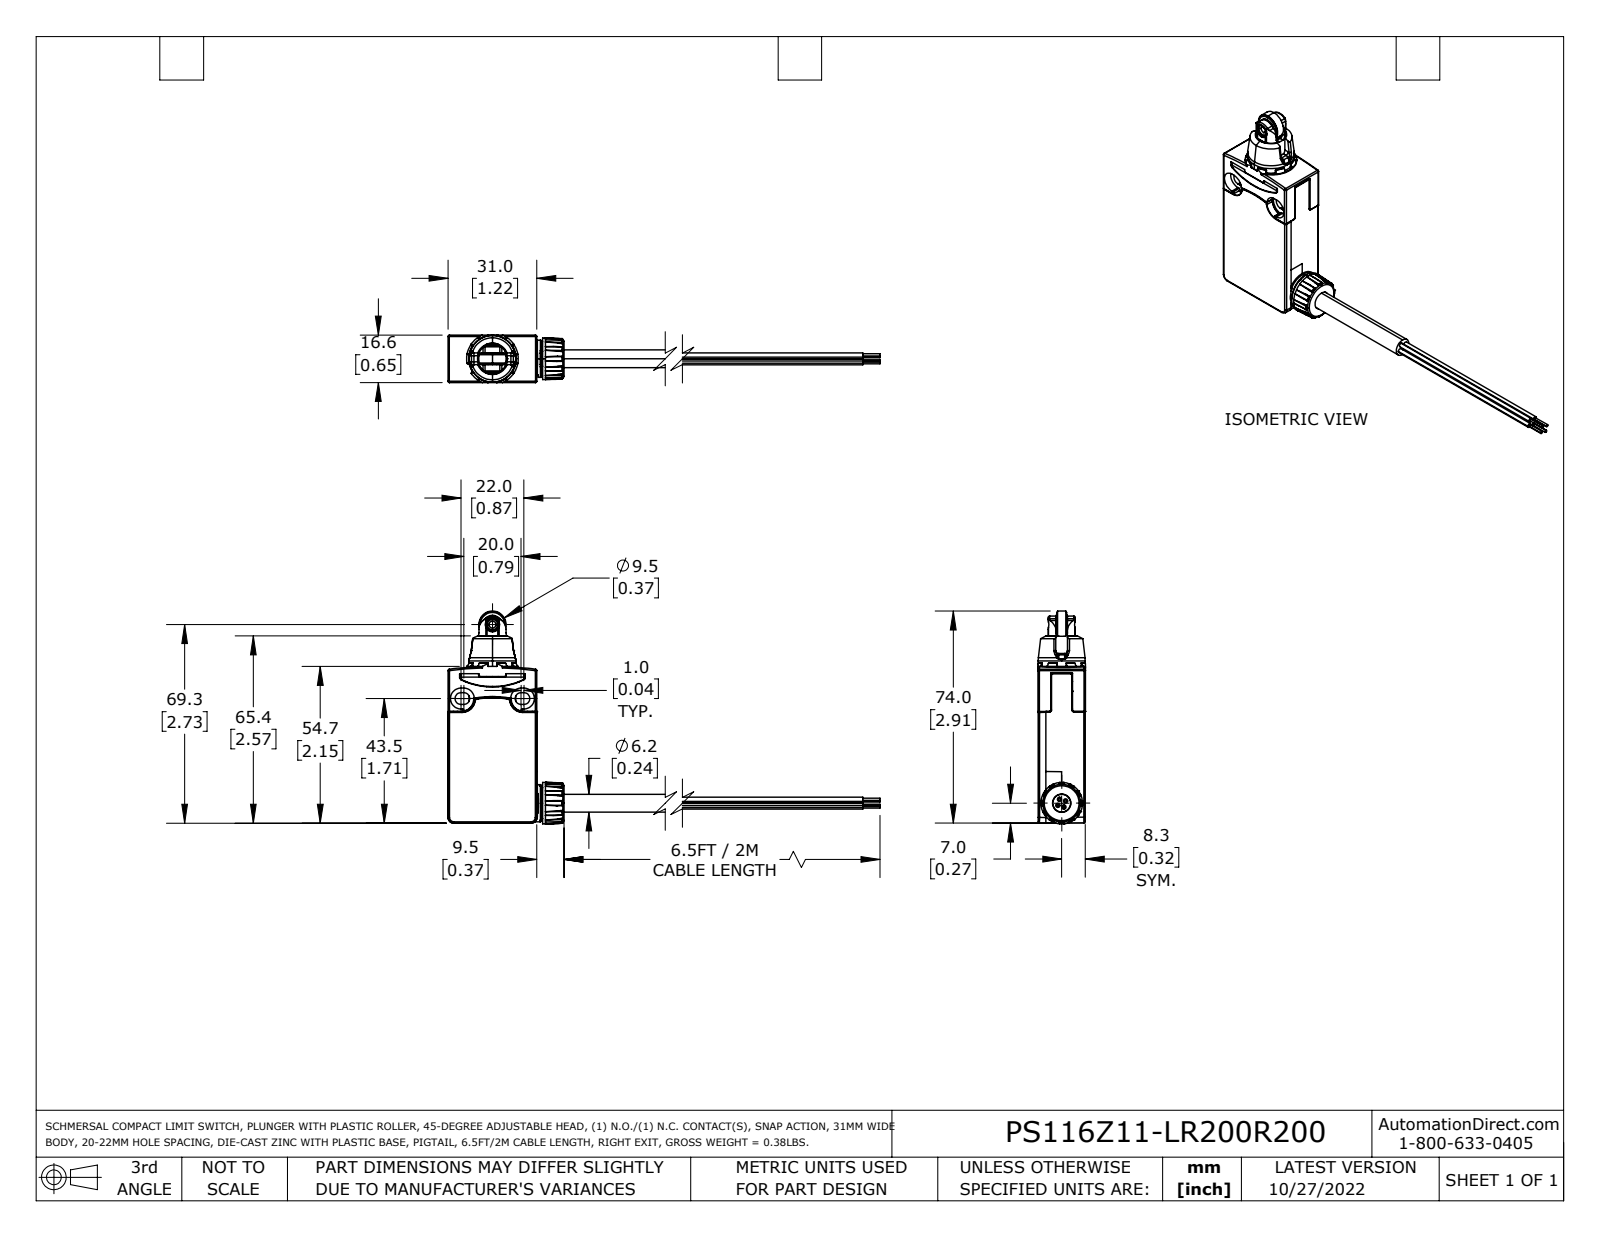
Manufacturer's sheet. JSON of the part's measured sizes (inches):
{"part_name": "PS116Z11-LR200R200_Default", "step_written_by": "SolidWorks 2021 (CONFIG_CONTROL_DESIGN)", "units": "inches", "bodies": {"solids": 2, "faces": 1214, "planar": 350, "cylindrical": 504, "other": 360}, "overall_size": [5.925, 2.926, 0.654], "volume_in3": 1.859, "surface_area_in2": 22.73, "round_holes": [[0.079, 1], [0.094, 1], [0.124, 1], [0.138, 1], [0.197, 1], [0.252, 1], [0.264, 1], [0.457, 1], [0.48, 1], [0.571, 1]], "round_bosses_or_shafts": [[0.059, 4], [0.031, 4], [0.512, 2], [0.646, 1], [0.571, 1], [0.567, 1], [0.524, 1], [0.449, 1]], "partial_cylinders_radius": [[0.008, 144], [0.004, 73], [0.02, 38], [0.039, 22], [0.014, 10], [0.012, 6], [0.079, 5], [0.081, 4]], "face_to_face_distances": [0.65, 0.652, 1.22, 0.067, 0.118, 0.116, 0.654, 0.138, 0.22, 0.024], "hole_center_spacings": [1.615]}
